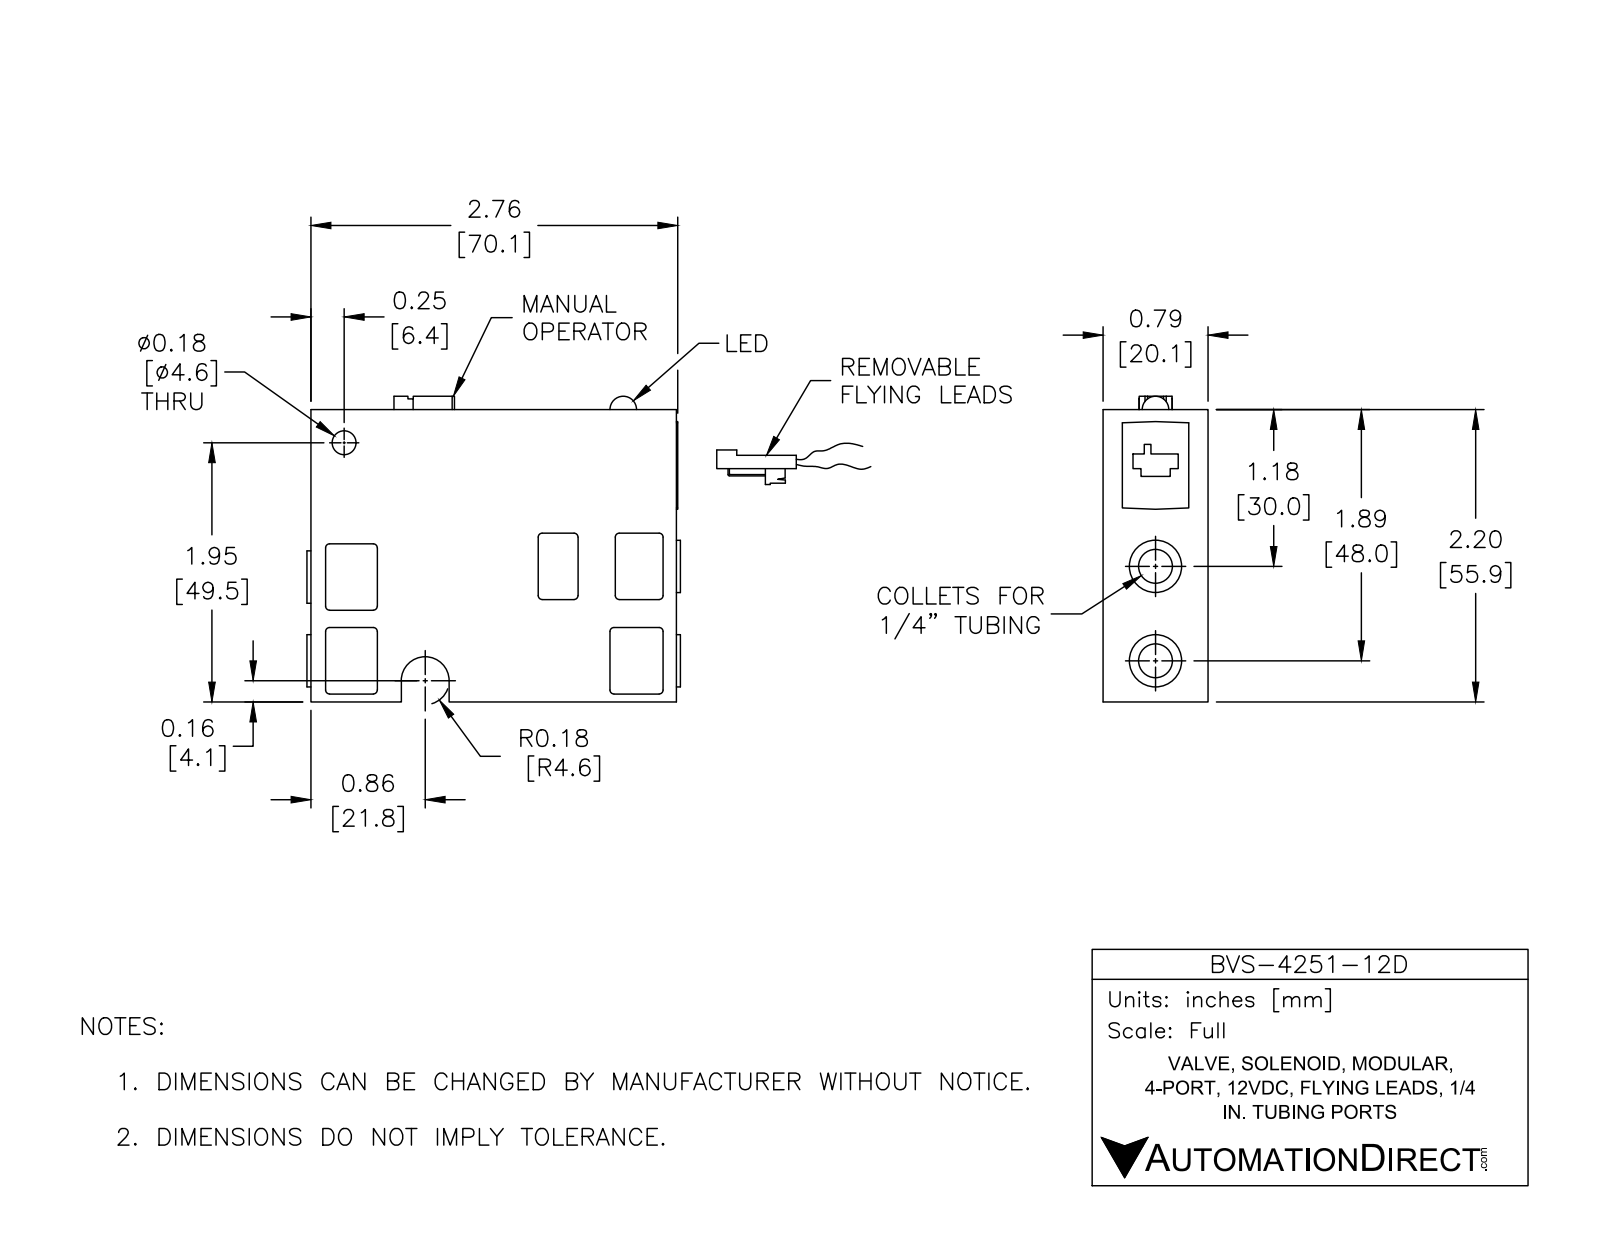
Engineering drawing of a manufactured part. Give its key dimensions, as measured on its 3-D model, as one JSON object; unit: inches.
{"part_name": "BVS-4251-12D", "step_written_by": "SolidWorks 2016 (AUTOMOTIVE_DESIGN)", "units": "inches", "bodies": {"solids": 1, "faces": 173, "planar": 85, "cylindrical": 78, "other": 10}, "overall_size": [3.009, 2.3, 0.79], "volume_in3": 4.372, "surface_area_in2": 25.08, "round_holes": [[0.254, 3], [0.1, 1], [0.18, 1]], "round_bosses_or_shafts": [[0.06, 6], [0.394, 3]], "partial_cylinders_radius": [[0.03, 20], [0.02, 2], [0.125, 1], [0.18, 1]], "face_to_face_distances": [0.79, 0.1, 2.2, 0.69, 2.75, 0.59, 0.5, 0.11, 2.65, 2.76], "hole_center_spacings": [0.08, 0.55, 0.63, 0.63, 0.71, 1.26]}
